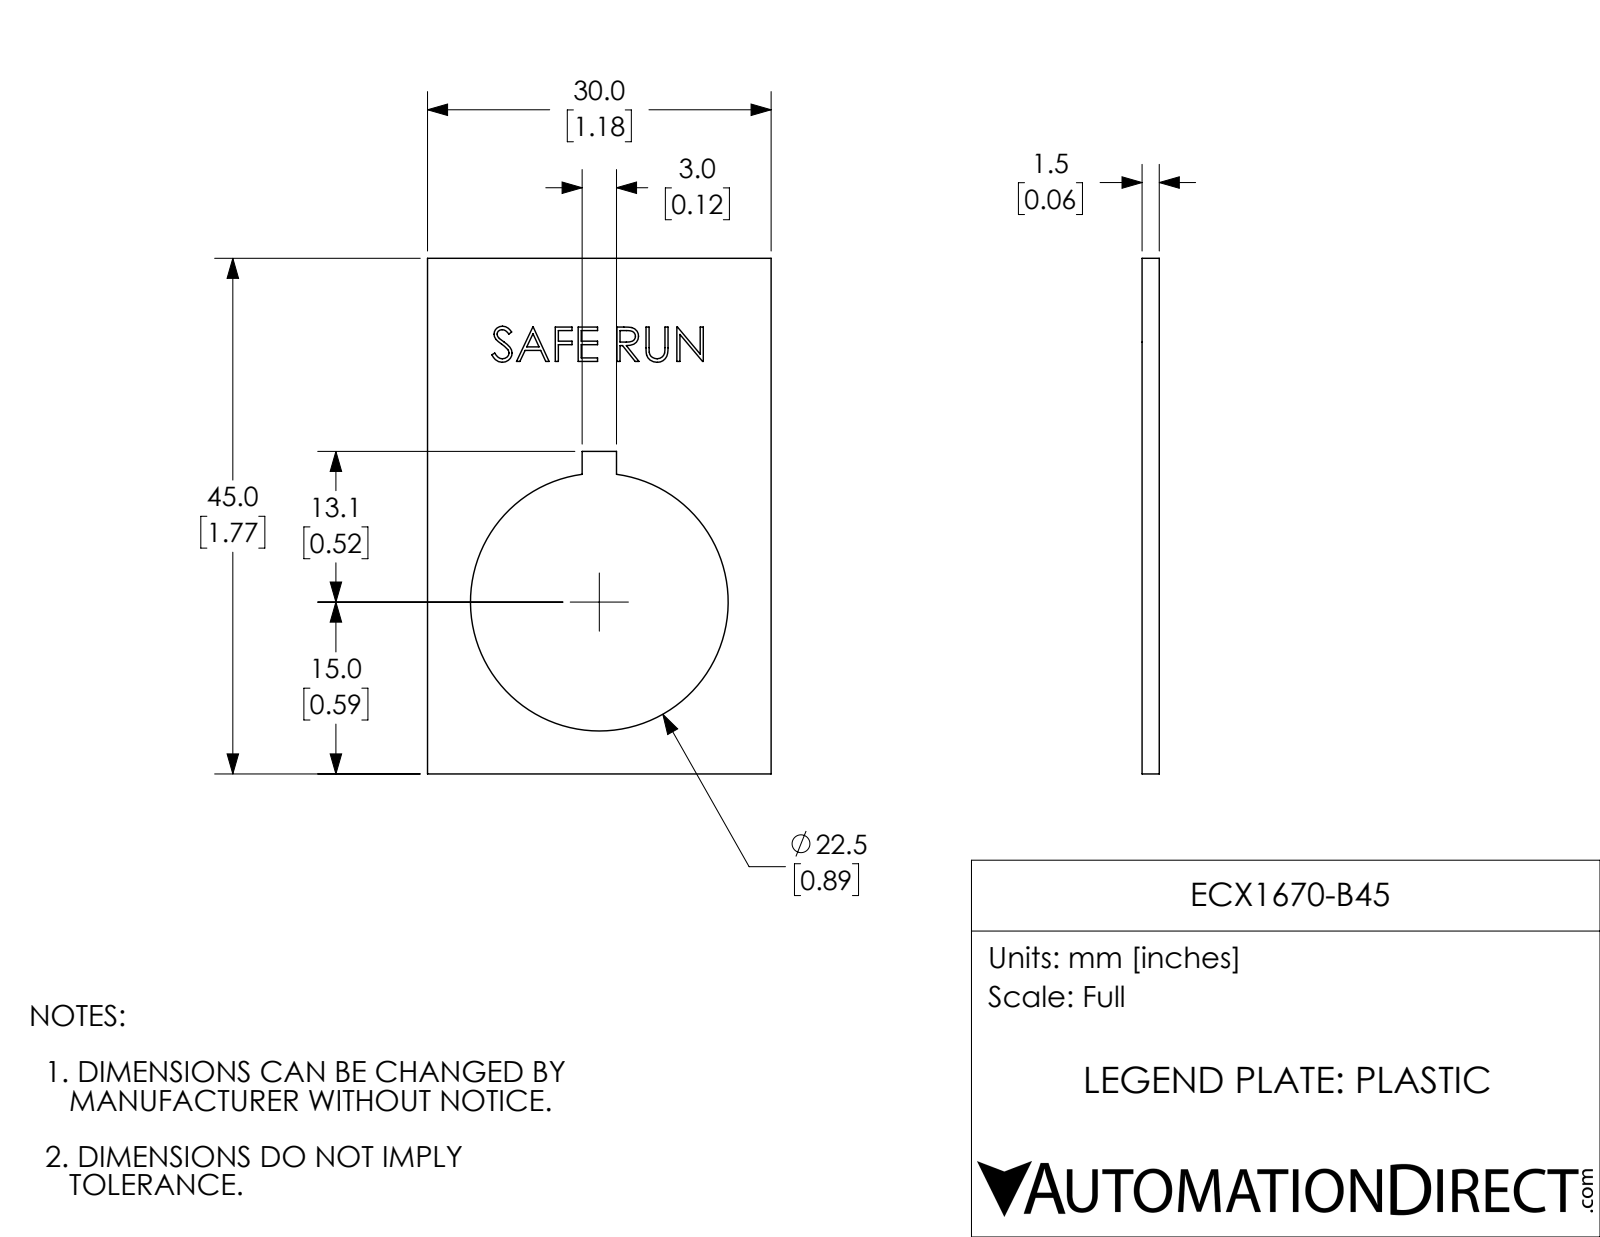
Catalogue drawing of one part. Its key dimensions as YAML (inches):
part_name: "ECX1670-B45"
step_written_by: "SolidWorks 2017 (AUTOMOTIVE_DESIGN)"
units: inches
bodies: {solids: 1, faces: 110, planar: 80, cylindrical: 3, other: 27}
overall_size: [1.772, 1.181, 0.059]
volume: 0.087
surface_area: 3.461
round_holes:
  - {diameter: 0.886, count: 1}
face_to_face_distances: [0.059, 1.181, 1.772, 0.058, 0.531, 0.65, 0.663, 1.108, 0.118, 0.012]
